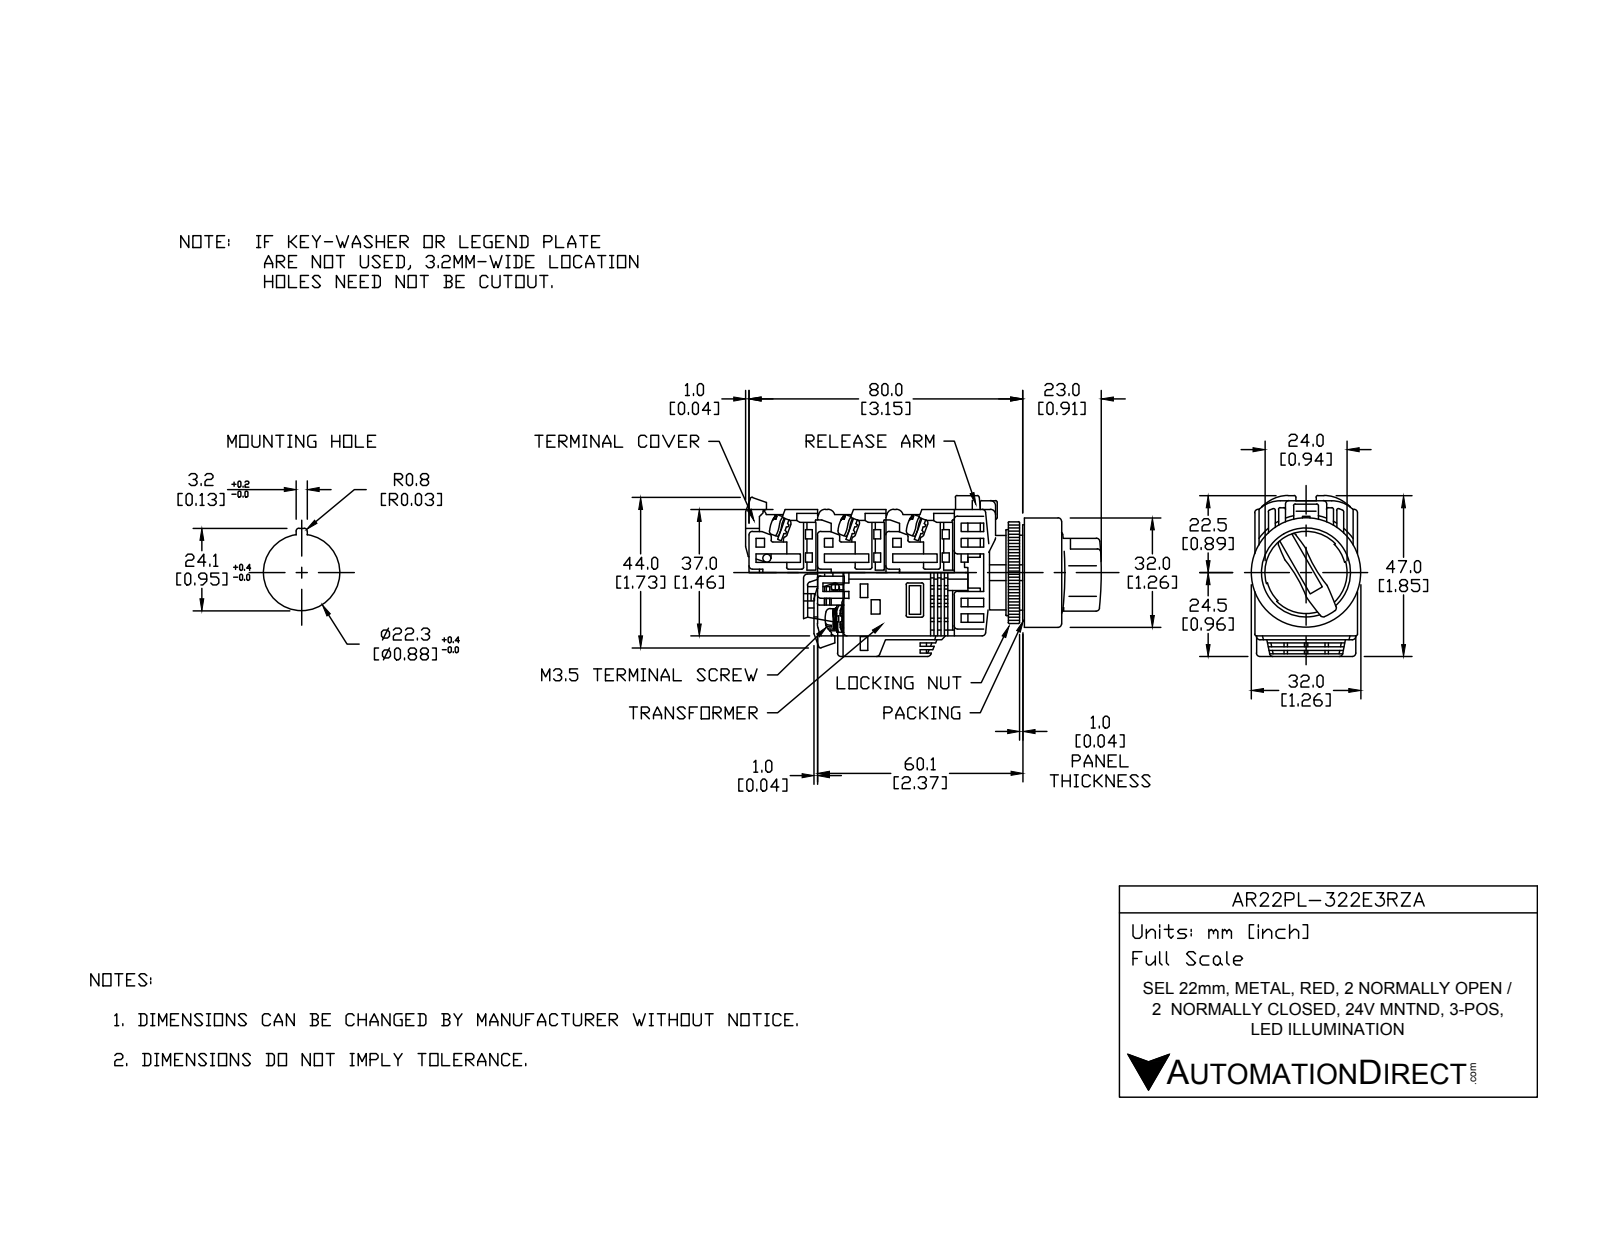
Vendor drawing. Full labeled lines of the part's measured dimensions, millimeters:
Part name (STEP PRODUCT): AR22PL-322E3RZA
STEP written by: SolidWorks 2017 (AUTOMOTIVE_DESIGN)
Units: millimetres
Bodies: 33 solids, 744 faces (524 planar, 181 cylindrical, 39 other)
Overall size (bounding box): 104.5 × 43.81 × 32
Volume: 64 125 mm³ · Surface area: 35 355 mm²
Round holes (diameter × count): ⌀21.8 ×1, ⌀22 ×1, ⌀25 ×1, ⌀31 ×1
Round bosses / shafts (diameter × count): ⌀5 ×10, ⌀32 ×1, ⌀30.5 ×1, ⌀29.8 ×1, ⌀24 ×1, ⌀21.75 ×1, ⌀17 ×1
Partial cylindrical surfaces — rounded edges, fillets, slot ends (radius × count): R0.5 ×66, R1.75 ×8, R1 ×6, R5 ×4, R4 ×2, R12 ×1, R16.59 ×1, R17.59 ×1
Main face-to-face distances: 20, 1, 18, 40, 29, 3, 9, 10, 2, 19
